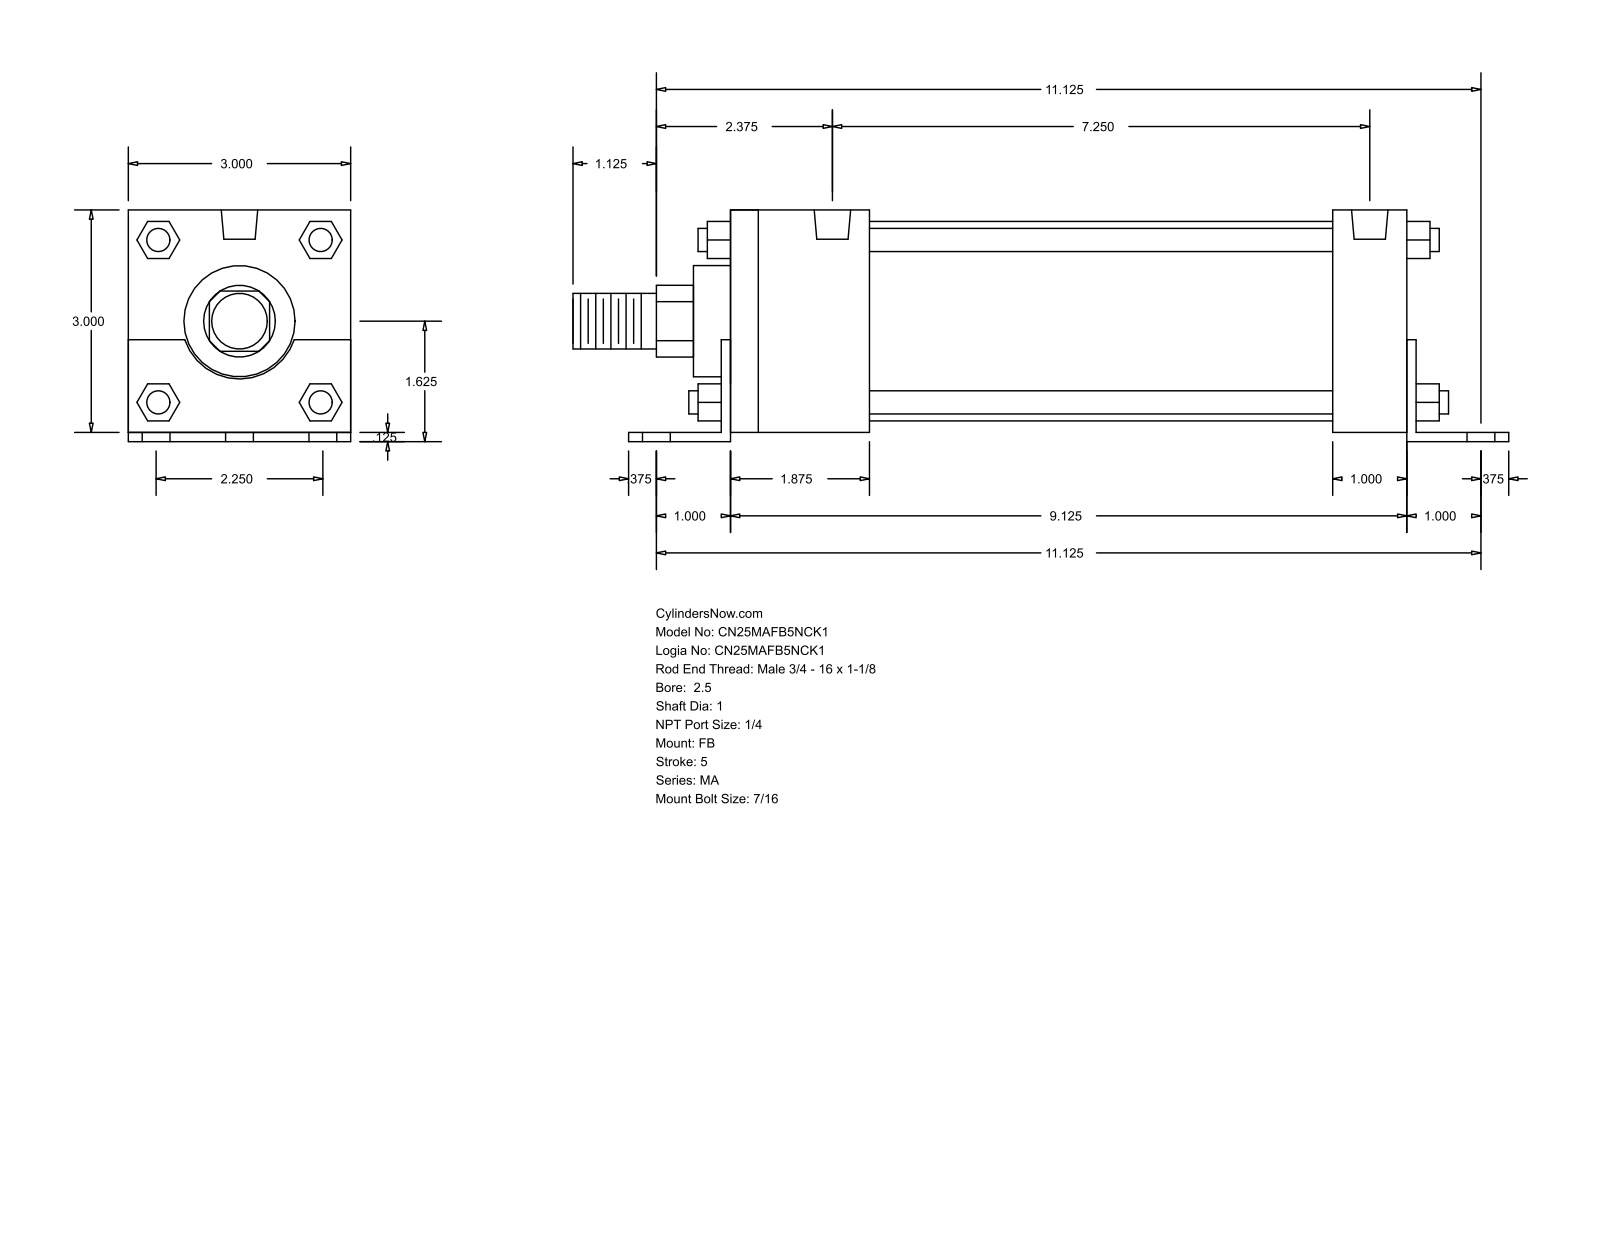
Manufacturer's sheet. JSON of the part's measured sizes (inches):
{"part_name": "MA_FB__0250_1", "step_written_by": "GSSL Pune (CONFIG_CONTROL_DESIGN)", "units": "inches", "bodies": {"solids": 0, "faces": 140, "planar": 105, "cylindrical": 35, "other": 0}, "overall_size": [12.625, 3.125, 3], "round_holes": [[0.437, 6], [0.313, 4], [0.492, 2]], "round_bosses_or_shafts": [[0.313, 4], [2.69, 1], [1.5, 1], [1, 1], [0.75, 1]], "partial_cylinders_radius": [[0.484, 1], [0.78, 1]], "face_to_face_distances": [3, 0.125, 3.125, 9.25, 9.125, 0.5, 1.125, 1, 2, 1.875], "hole_center_spacings": [1.125, 11.181, 11.125, 1.875, 2.25, 2.628, 7.25, 8.822]}
